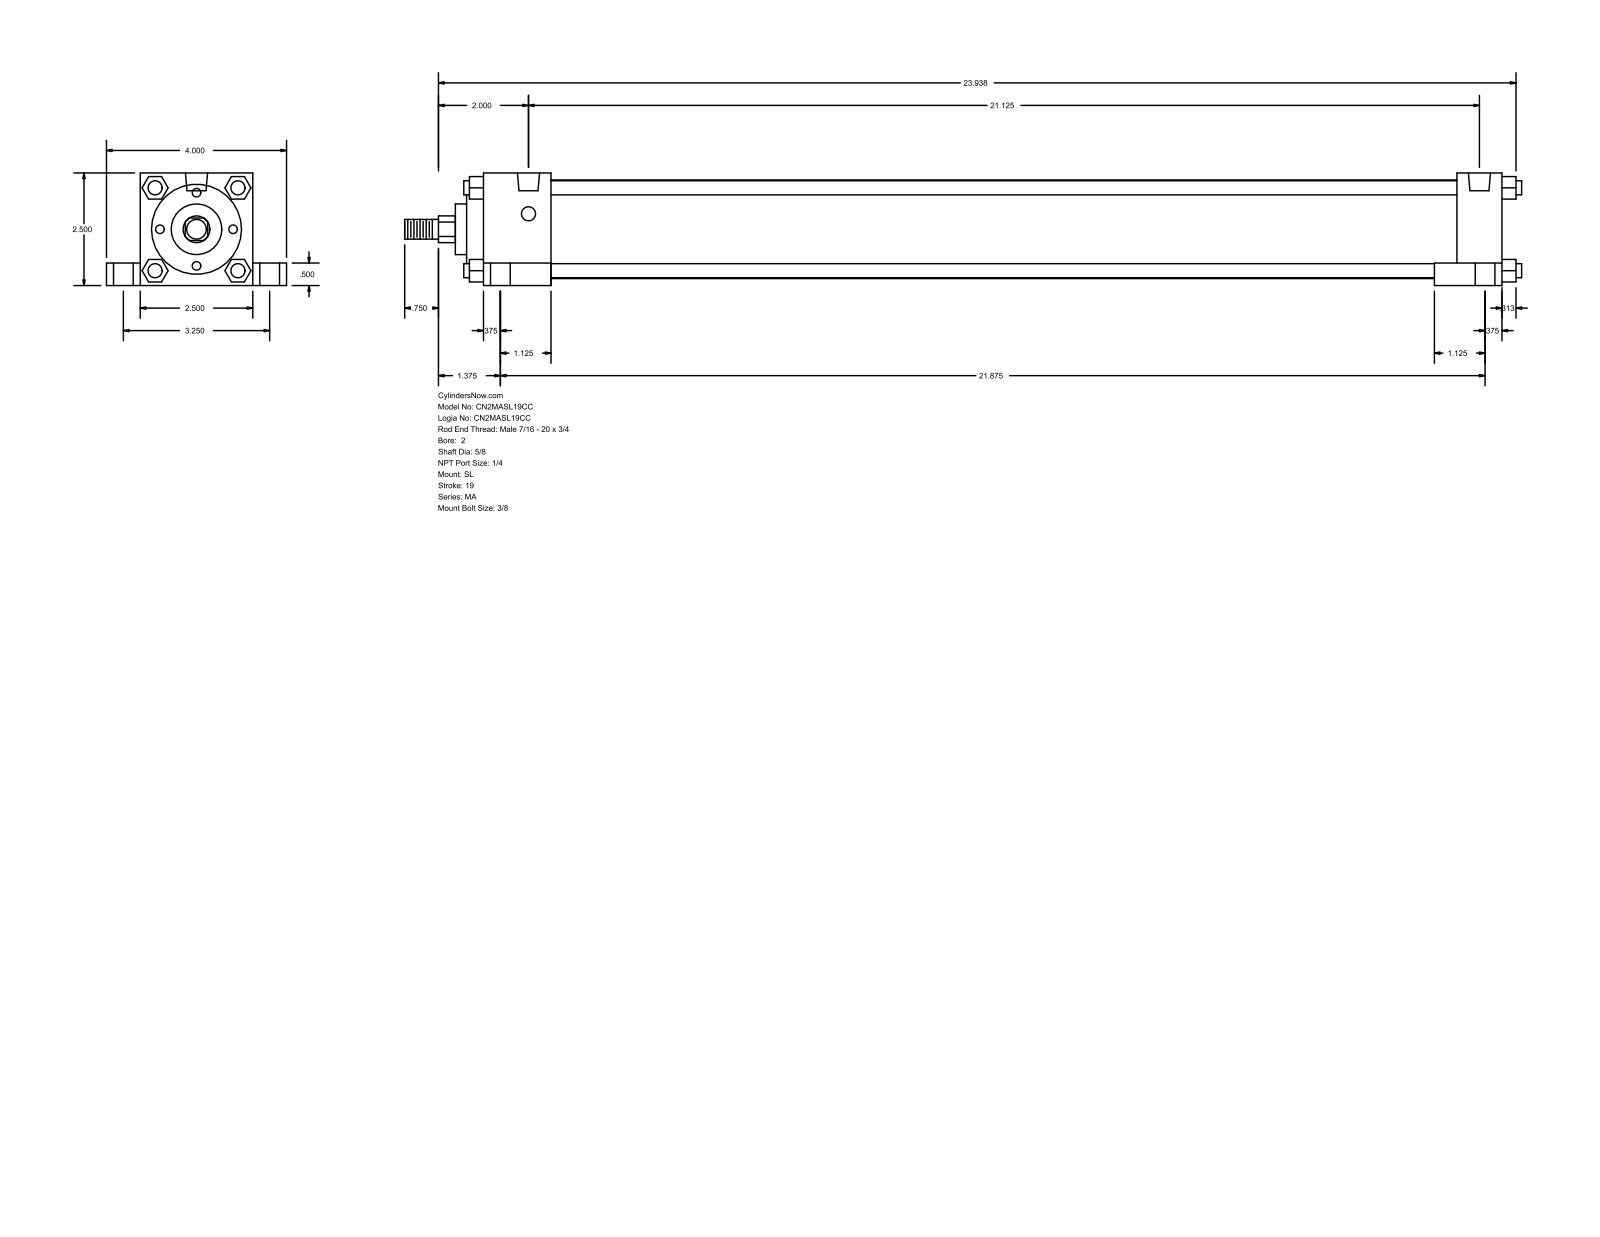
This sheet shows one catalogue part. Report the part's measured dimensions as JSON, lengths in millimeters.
{"part_name": "MA_SL__0200_0.625", "step_written_by": "GSSL Pune (CONFIG_CONTROL_DESIGN)", "units": "millimeters", "bodies": {"solids": 0, "faces": 150, "planar": 113, "cylindrical": 37, "other": 0}, "overall_size": [630.24, 101.6, 63.5], "round_holes": [[7.94, 4], [11.11, 4], [17.46, 4], [12.49, 2]], "round_bosses_or_shafts": [[7.94, 4], [55.63, 1], [50.8, 1], [28.57, 1], [15.88, 1], [11.11, 1]], "partial_cylinders_radius": [[7.54, 1]], "face_to_face_distances": [63.5, 12.7, 9.52, 511.17, 19.05, 82.55, 38.1, 50.8, 574.68, 536.58], "hole_center_spacings": [41.39, 44.22, 82.54, 536.58, 541.33, 554, 555.63, 561.73]}
